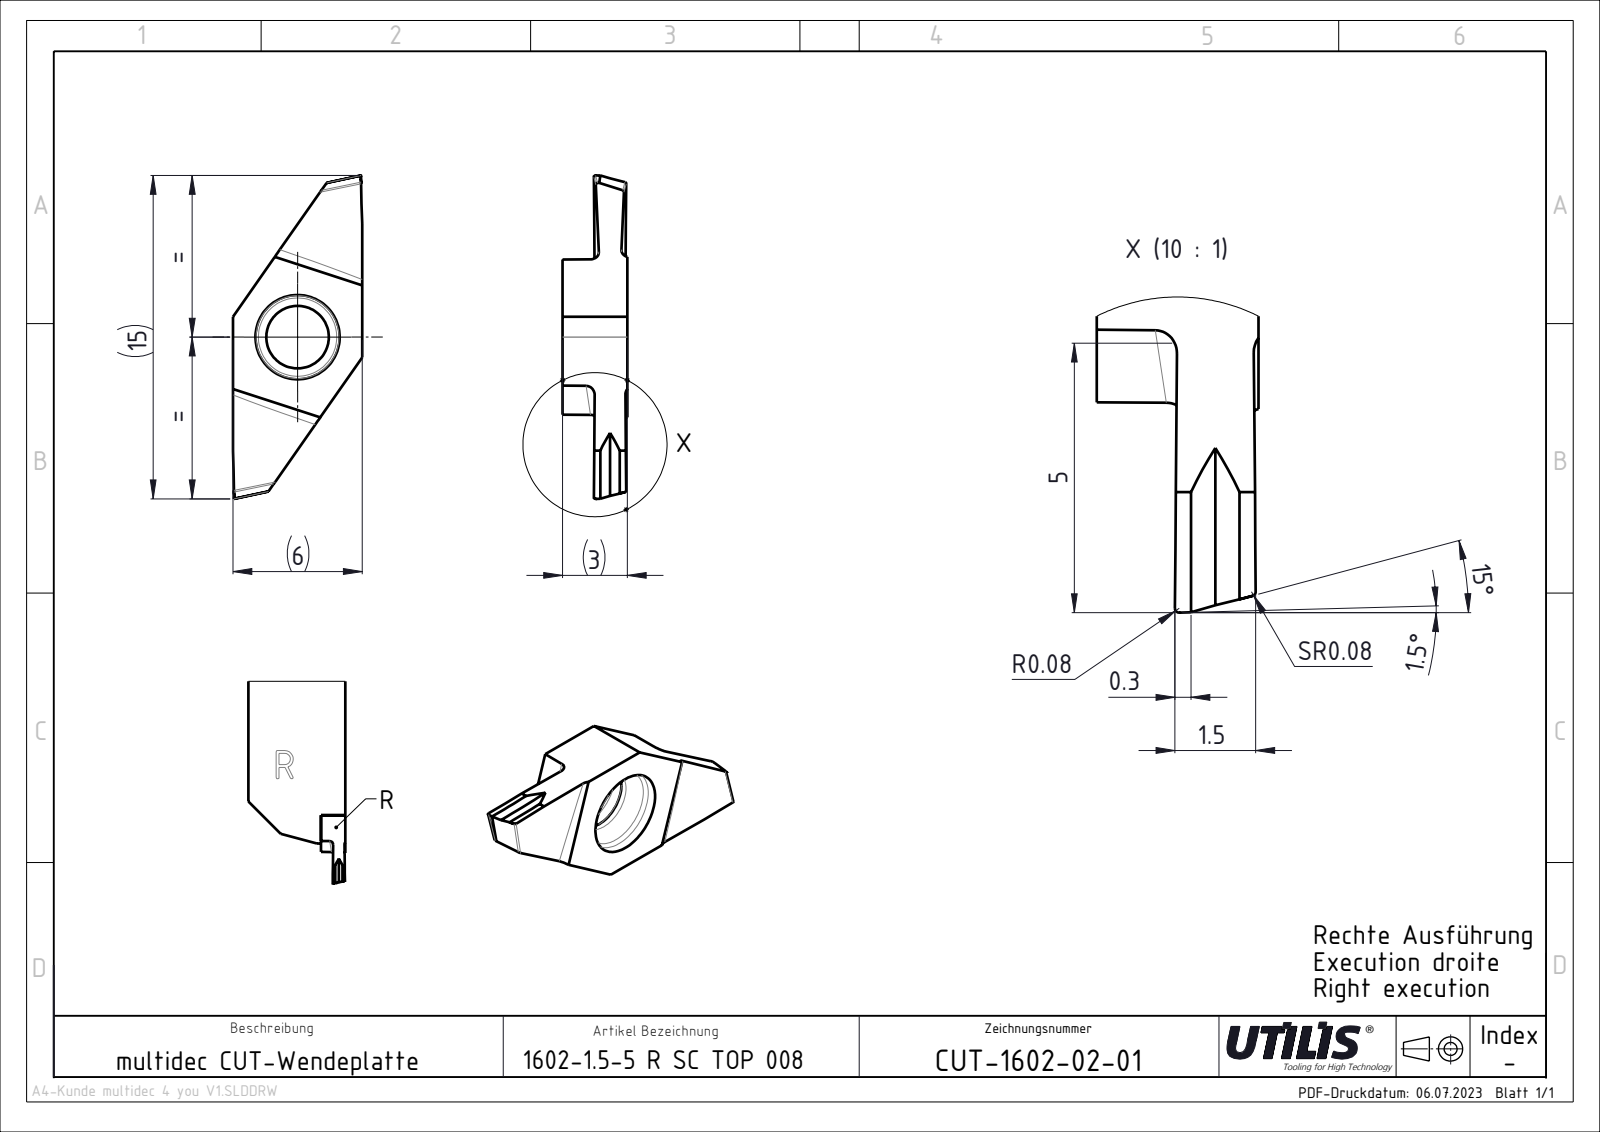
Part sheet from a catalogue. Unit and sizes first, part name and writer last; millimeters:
Units: millimetres
Overall size (bounding box): 15 × 6 × 3
Round holes (diameter × count): ⌀2.9 ×1
Partial cylindrical surfaces — rounded edges, fillets, slot ends (radius × count): R0.4 ×4
Main face-to-face distances: 6, 3, 1.34, 15
Volume: 118 mm³ · Surface area: 216 mm²
Bodies: 1 solid, 27 faces (18 planar, 9 cylindrical, 0 other)
Part name (STEP PRODUCT): 1602-CUT-1602-02-01 stp
STEP written by: SolidWorks 2022 (AUTOMOTIVE_DESIGN)
